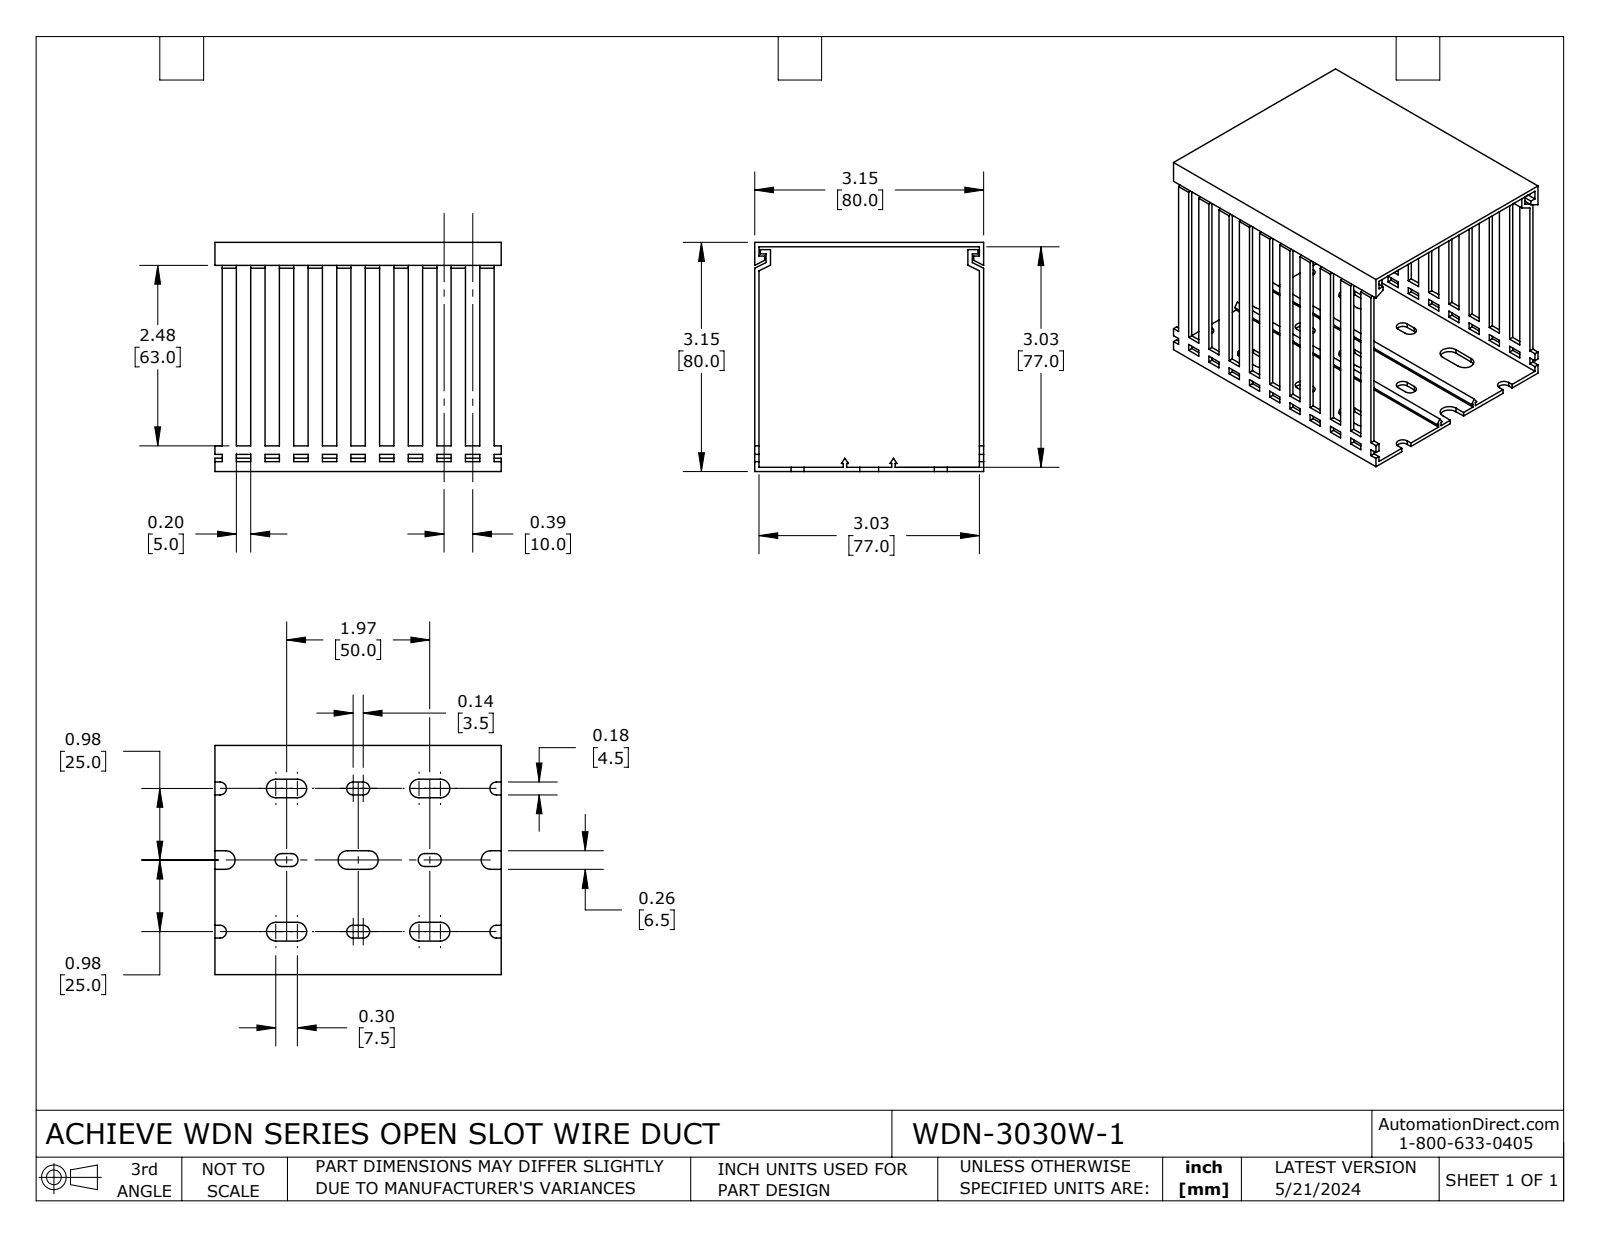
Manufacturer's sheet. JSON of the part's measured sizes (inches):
{"part_name": "WDN-3030W-1", "step_written_by": "SolidWorks 2023 (CONFIG_CONTROL_DESIGN)", "units": "inches", "bodies": {"solids": 2, "faces": 398, "planar": 362, "cylindrical": 36, "other": 0}, "overall_size": [3.937, 3.15, 3.15], "volume_in3": 2.393, "surface_area_in2": 91.08, "partial_cylinders_radius": [[0.089, 12], [0.128, 12]], "face_to_face_distances": [0.059, 3.091, 3.15, 3.031, 0.197, 0.394, 0.591, 0.787, 0.984, 1.181]}
